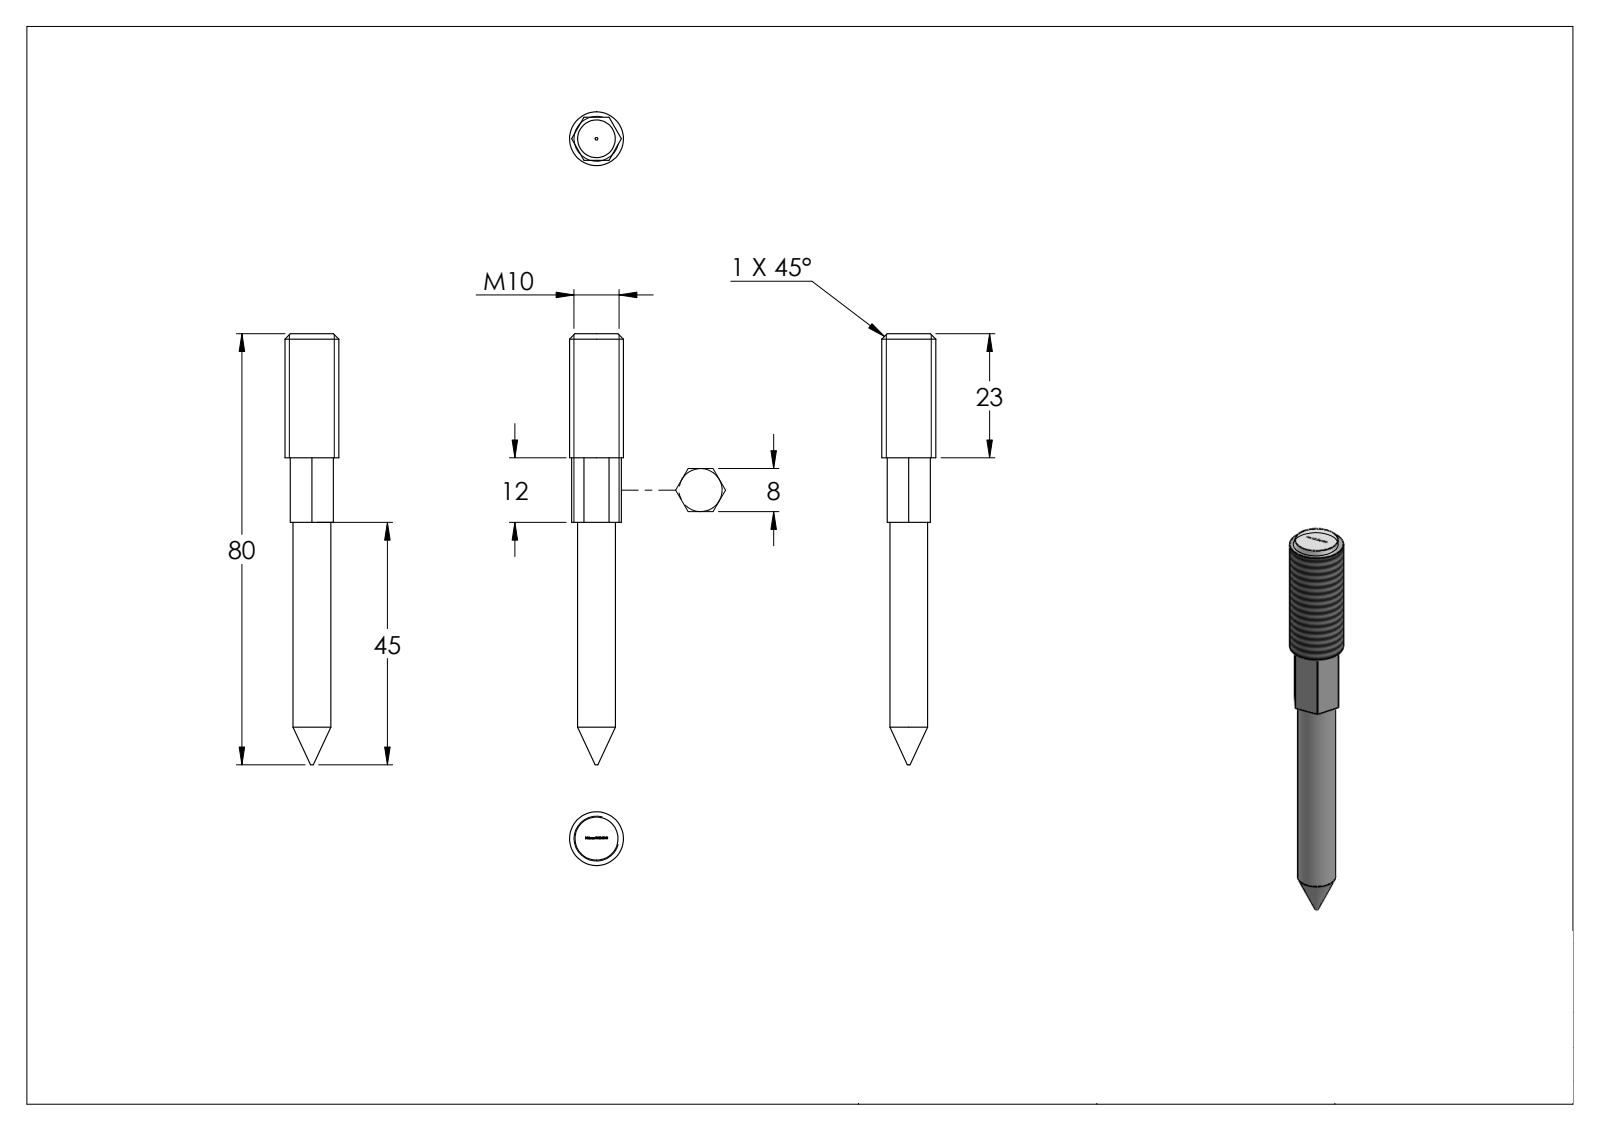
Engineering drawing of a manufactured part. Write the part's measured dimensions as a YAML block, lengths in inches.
part_name: "58342-240-80"
step_written_by: "SolidWorks 2018 (CONFIG_CONTROL_DESIGN)"
units: inches
bodies: {solids: 1, faces: 292, planar: 150, cylindrical: 4, other: 138}
overall_size: [3.15, 0.394, 0.394]
volume: 0.245
surface_area: 3.229
round_bosses_or_shafts:
  - {diameter: 0.394, count: 1}
  - {diameter: 0.276, count: 1}
face_to_face_distances: [0.315, 0.906, 0.472, 1.378, 1.374, 0.902, 1.772, 2.244, 3.146, 3.15]
